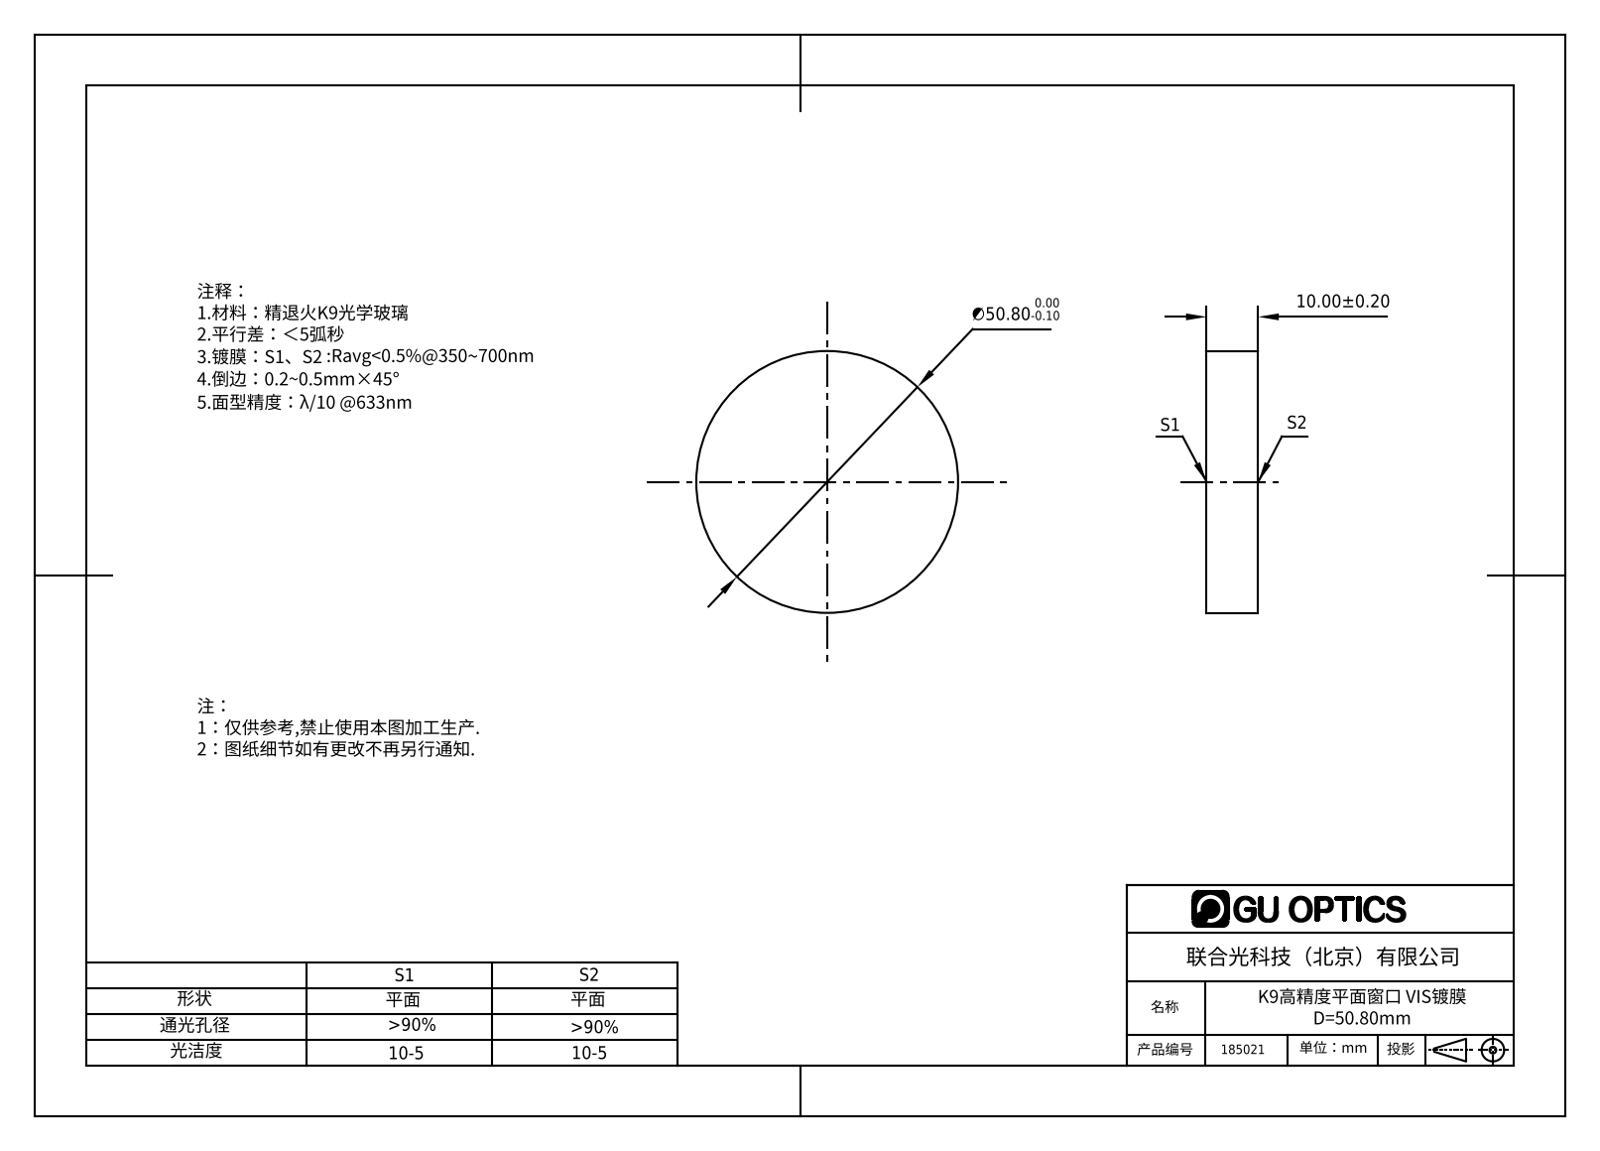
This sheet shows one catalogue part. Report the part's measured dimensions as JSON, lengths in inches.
{"part_name": "185010", "step_written_by": "SolidWorks 2016 (AUTOMOTIVE_DESIGN)", "units": "inches", "bodies": {"solids": 1, "faces": 4, "planar": 2, "cylindrical": 2, "other": 0}, "overall_size": [2, 2, 0.394], "volume_in3": 1.237, "surface_area_in2": 8.758, "round_bosses_or_shafts": [[2, 1]], "face_to_face_distances": [0.394]}
